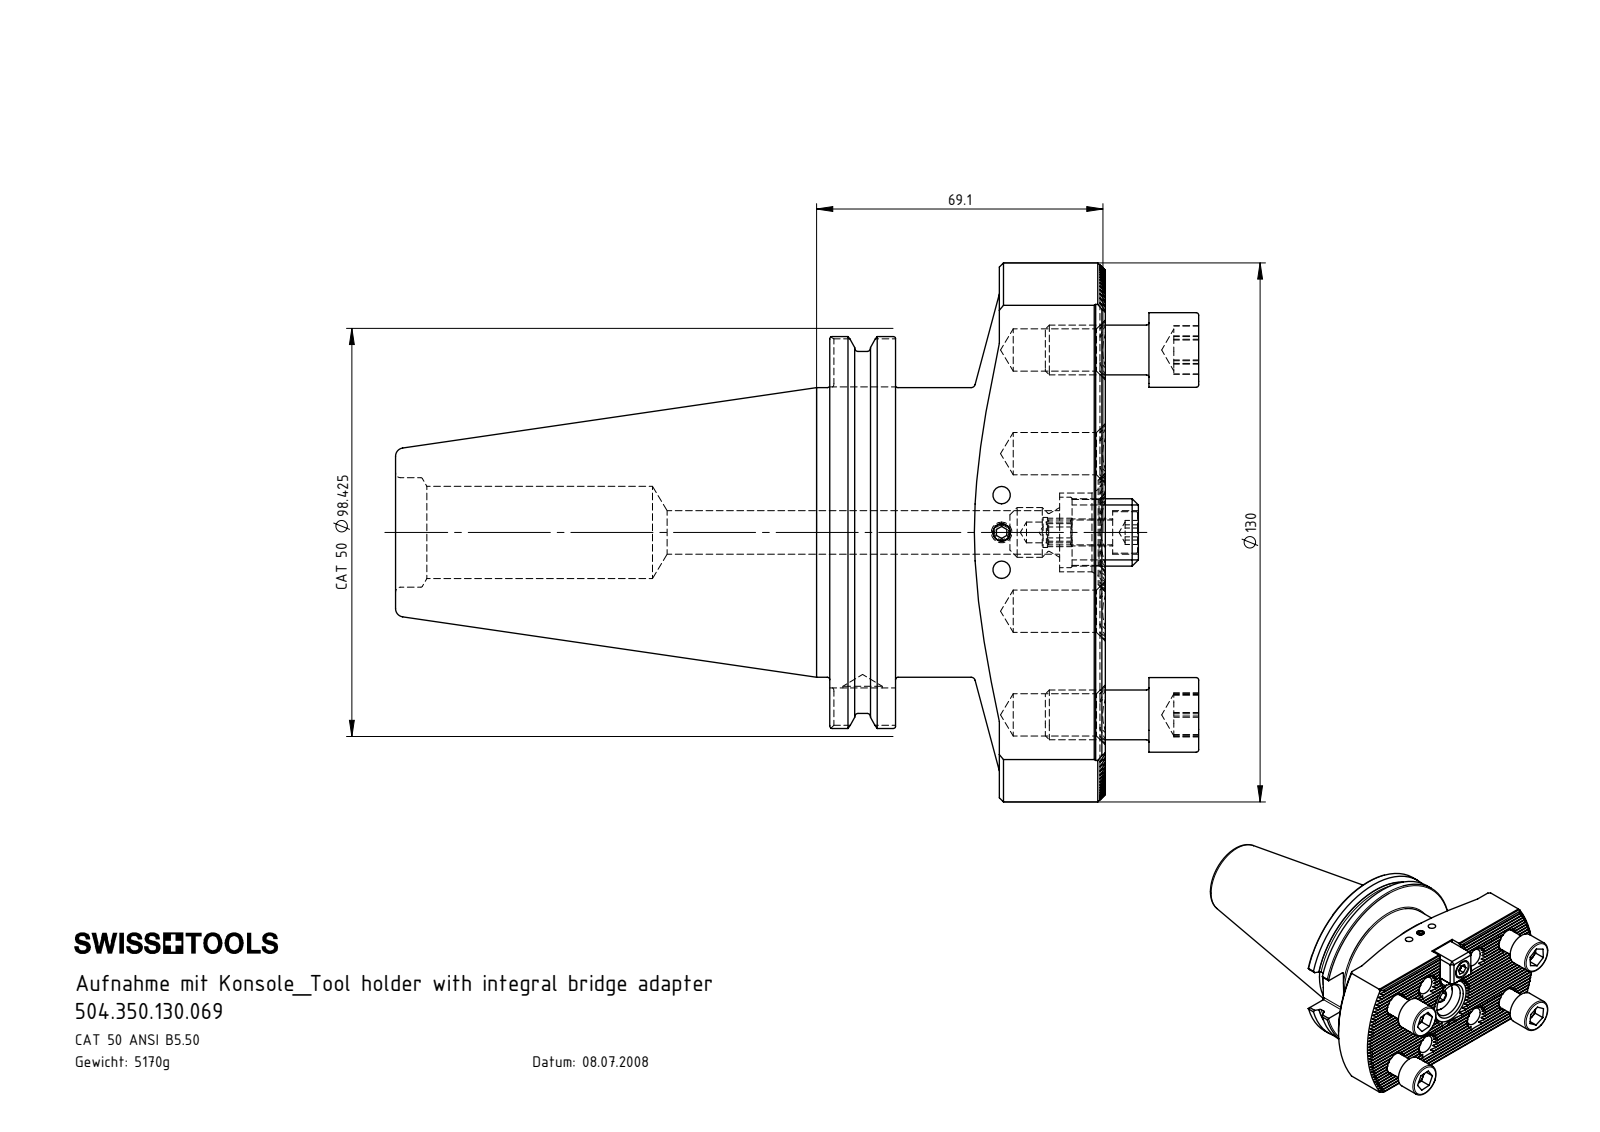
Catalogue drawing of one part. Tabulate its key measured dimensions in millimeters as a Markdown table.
| quantity | value |
| --- | --- |
| part name | ISO 4026 - M5 x 8; DIN 908 - M12x1.5; ISO 4762 - M12 x 25; ISO 4762 - M6 x 16 (+3 more) |
| STEP written by | SolidWorks 2017 (CONFIG_CONTROL_DESIGN) |
| units | millimeters |
| bodies | 10 solids, 859 faces (495 planar, 201 cylindrical, 163 other) |
| overall size | 195.62 × 130 × 98.42 |
| volume | 658 596 mm³ |
| surface area | 92 514 mm² |
| round holes (diameter × count) | 10.2 × 8, 4.2 × 3, 10.5 × 2, 5 × 1, 6.5 × 1, 7.24 × 1, 9.5 × 1, 19 × 1, 22.25 × 1, 26.4 × 1 |
| round bosses / shafts (diameter × count) | 12 × 5, 18 × 4, 98.42 × 1, 91 × 1, 69.85 × 1, 17 × 1, 10 × 1, 6 × 1 |
| partial cylindrical surfaces (radius × count) | 0.14 × 34, 0.8 × 8, 7.95 × 1, 65 × 1 |
| main face-to-face distances | 1.73, 17.32, 15.87, 70, 8.66, 3.46, 5.2, 6.93, 15.59, 19.05 |
| hole center spacings | 25, 27.59, 40, 47.17, 48.33, 63, 74.63, 9 |
